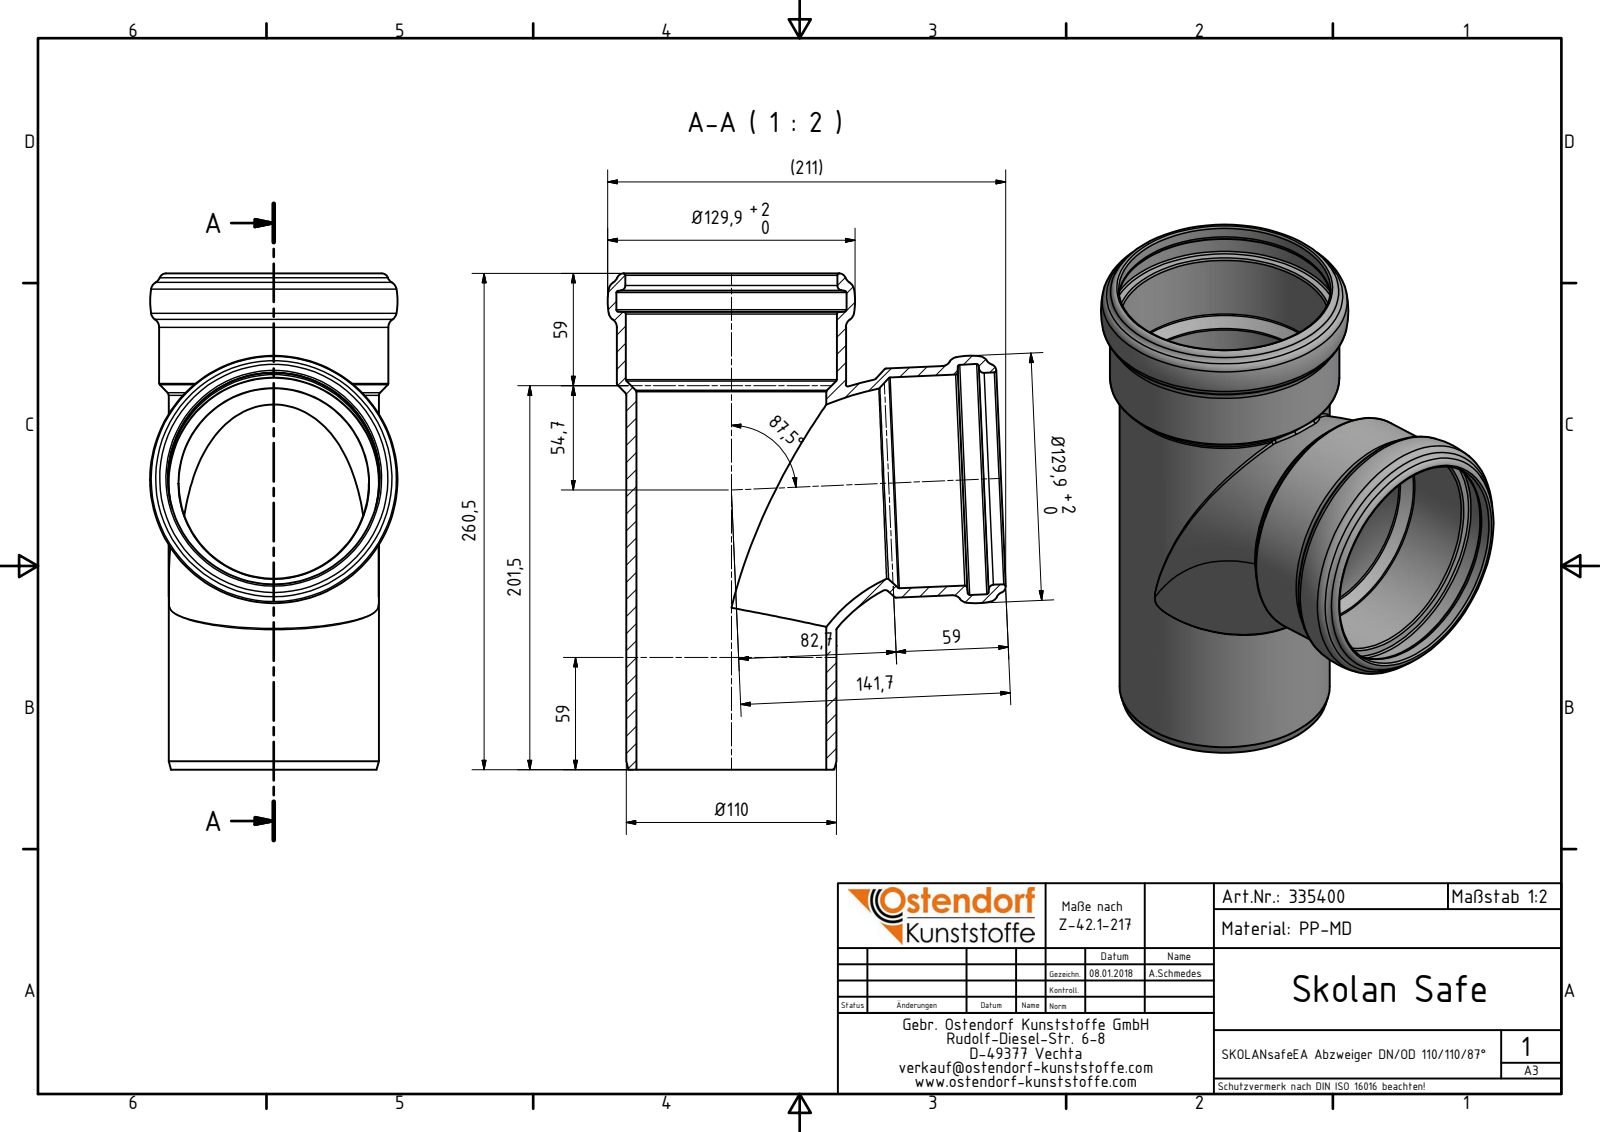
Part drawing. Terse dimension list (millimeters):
name: 335400 SKOLANsafeEA Abzweiger DN_OD 110_110_87°
written by: Autodesk Inventor 2016 (AUTOMOTIVE_DESIGN)
unit: mm
bodies: 1 solid, 58 faces (1 planar, 10 cylindrical, 47 other)
size: 260.5 × 208.99 × 129.9
volume: 610 315 mm³; area: 244 853 mm²
holes: 2× ⌀110.8, 2× ⌀111.3, 2× ⌀120.9, 1× ⌀99.8
bosses: 2× ⌀120.4, 1× ⌀110.4
